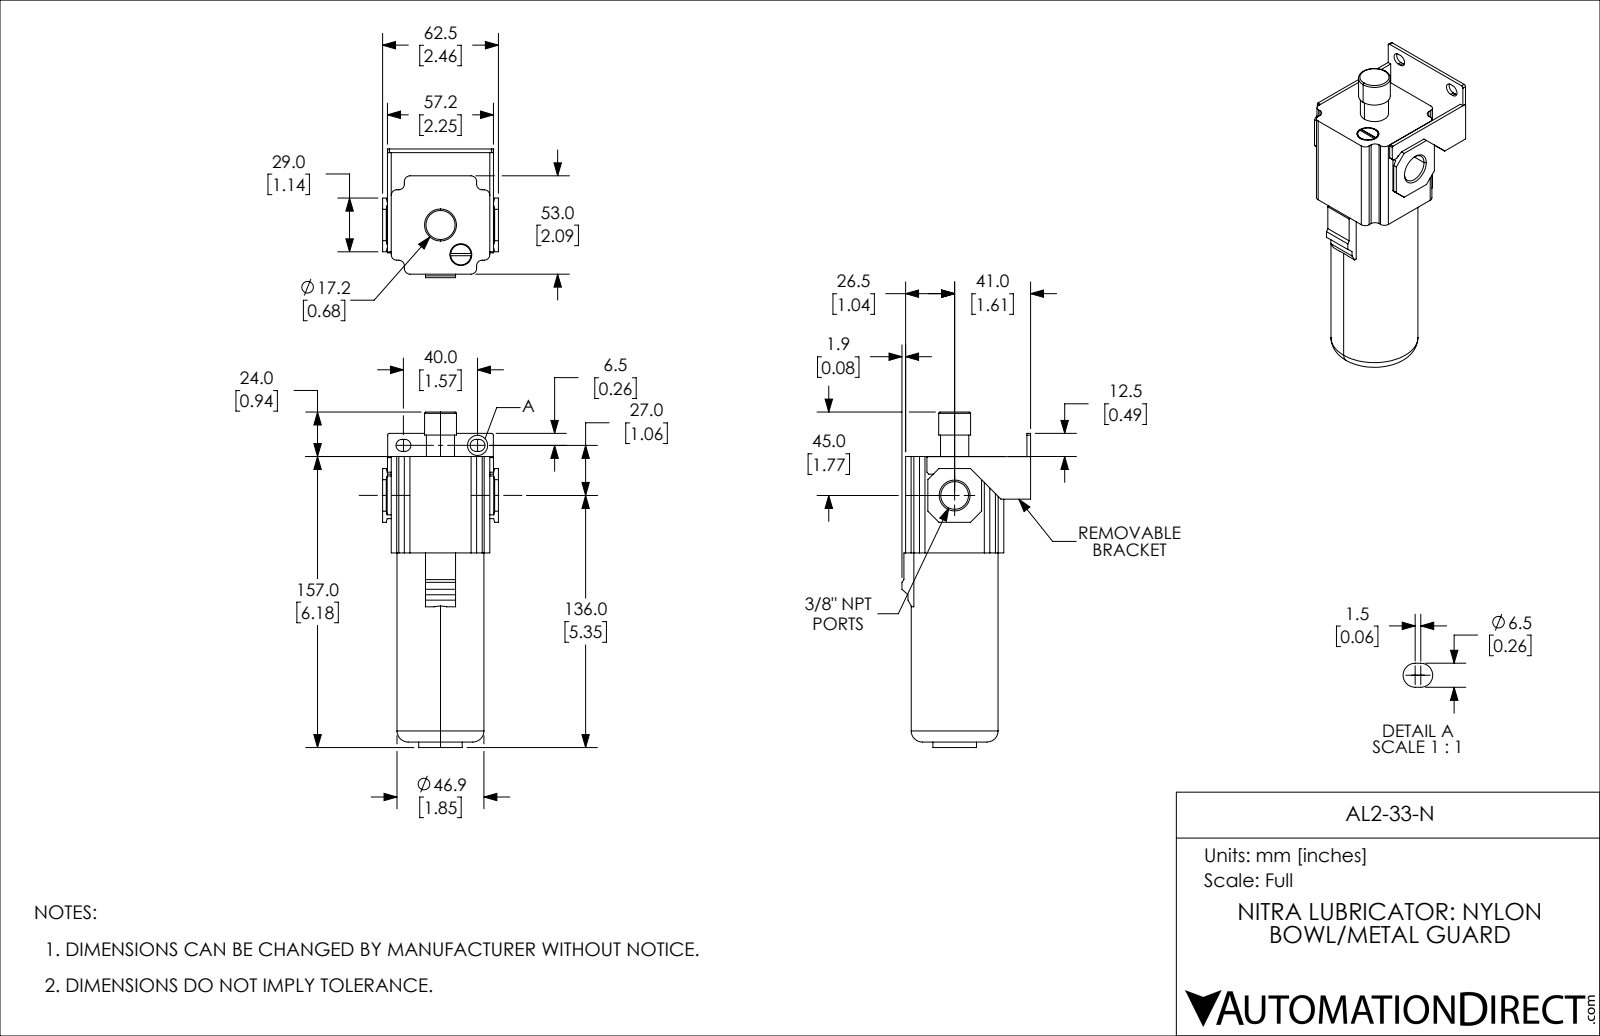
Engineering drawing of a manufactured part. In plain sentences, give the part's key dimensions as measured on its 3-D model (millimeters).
The part is named "AL2-33-N". Its 3-D file was written by "SolidWorks 2019 (CONFIG_CONTROL_DESIGN)". It is 1 solid with 138 faces: 96 planar, 34 cylindrical and 8 other. Overall it measures 181 by 69.42 by 62.5 millimeters. Its volume is 325 884 cubic millimeters and its surface area 41 369 square millimeters. Round holes: 1 of diameter 11.8, 1 of diameter 14.95. Round bosses or shafts: 1 of diameter 46.9, 1 of diameter 23.5, 1 of diameter 17.2, 1 of diameter 15.2, 1 of diameter 11. Partial cylindrical surfaces (rounded edges, fillets, slot ends): 12 of radius 3, 4 of radius 3.25, 2 of radius 1. The main face-to-face distances are 2, 12.5, 14.5, 67.5, 65.5, 53, 55.2, 53.2, 2.65, 4.65.
